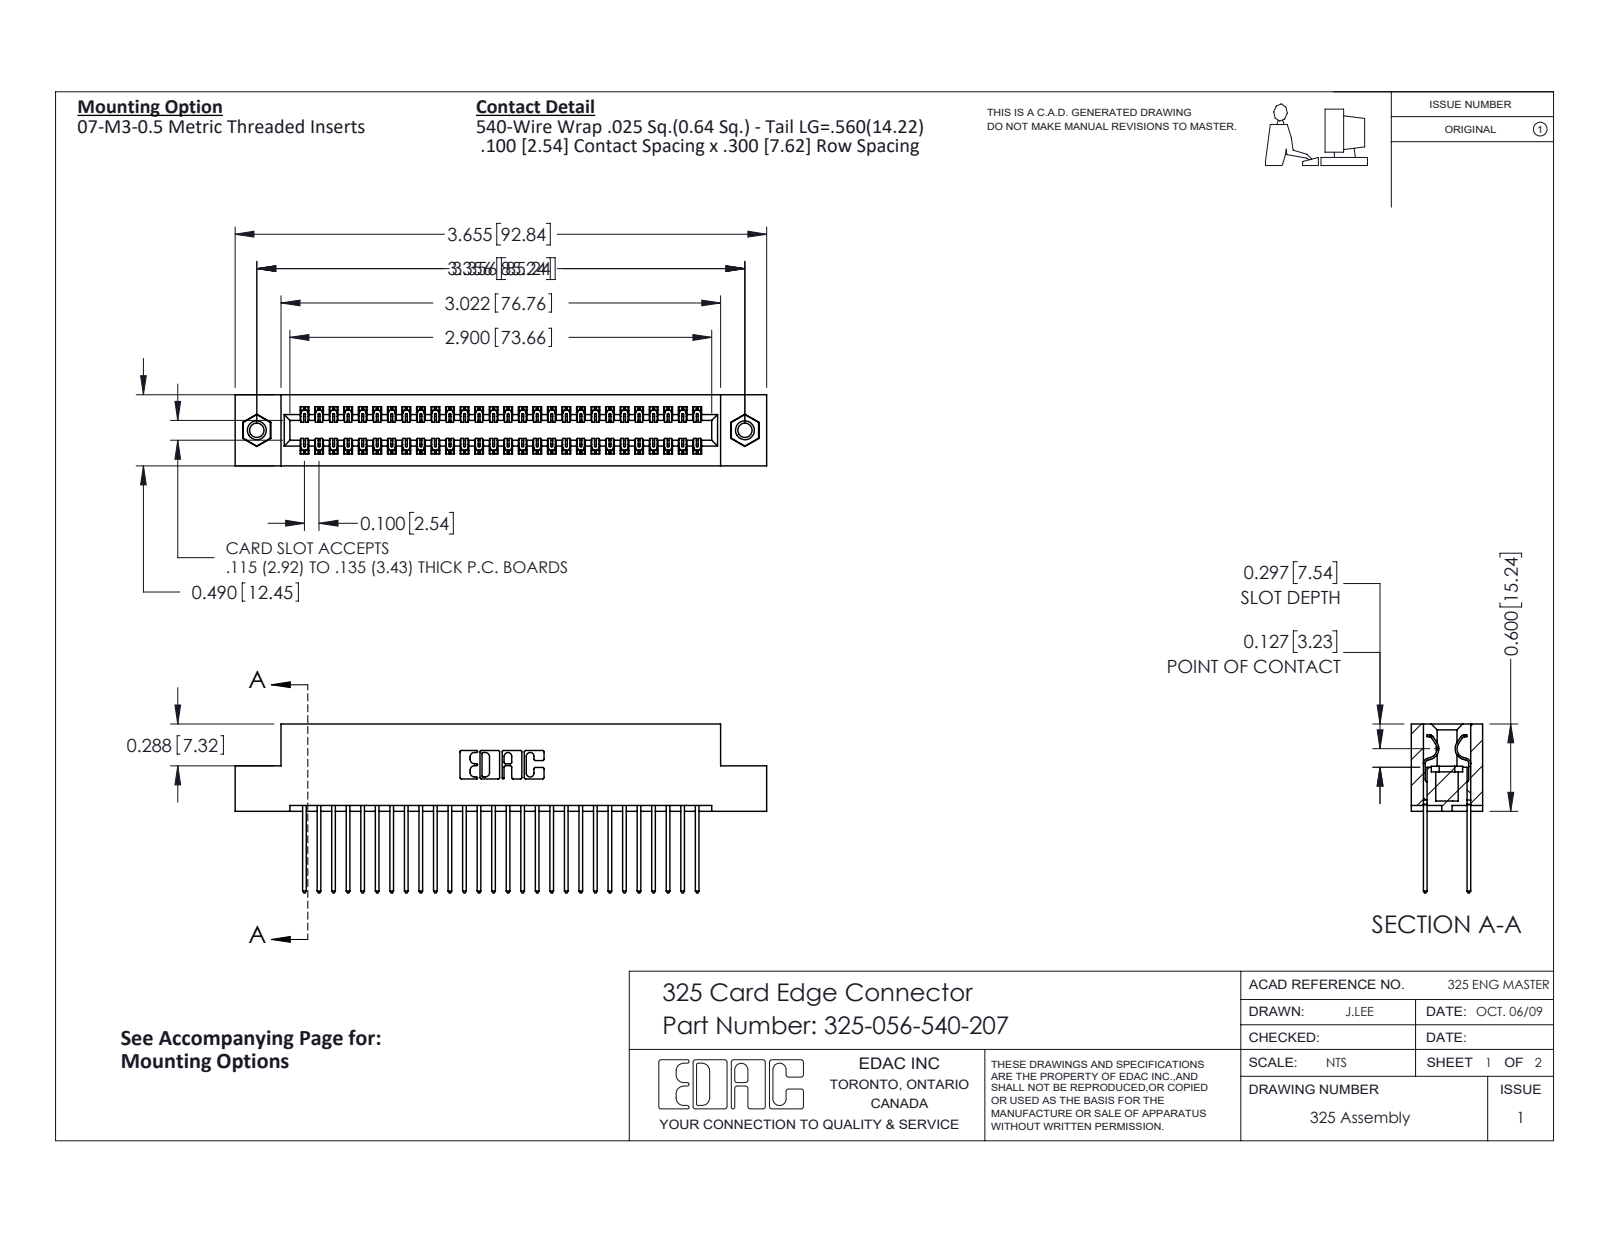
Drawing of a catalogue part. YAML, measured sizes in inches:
part_name: "325-292-001_325-293-140; 325-056-540-207; 345-250-001_345-250-005-103; 325 Part_TI"
step_written_by: "SolidWorks 2016 (CONFIG_CONTROL_DESIGN)"
units: inches
bodies: {solids: 59, faces: 3086, planar: 2118, cylindrical: 952, other: 16}
overall_size: [3.655, 1.16, 0.49]
volume: 0.736
surface_area: 23.71
round_holes:
  - {diameter: 0.098, count: 2}
  - {diameter: 0.125, count: 2}
  - {diameter: 0.16, count: 2}
round_bosses_or_shafts:
  - {diameter: 0.155, count: 2}
partial_cylinders:
  - {radius: 0.006, count: 84}
  - {radius: 0.01, count: 56}
  - {radius: 0.01, count: 22}
  - {radius: 0.007, count: 6}
  - {radius: 0.031, count: 6}
  - {radius: 0.026, count: 3}
  - {radius: 0.014, count: 2}
  - {radius: 0.022, count: 2}
face_to_face_distances: [0.083, 0.407, 0.3, 0.107, 0.383, 0.025, 0.49, 0.325, 0.275, 0.6]
hole_center_spacings: [3.356]
